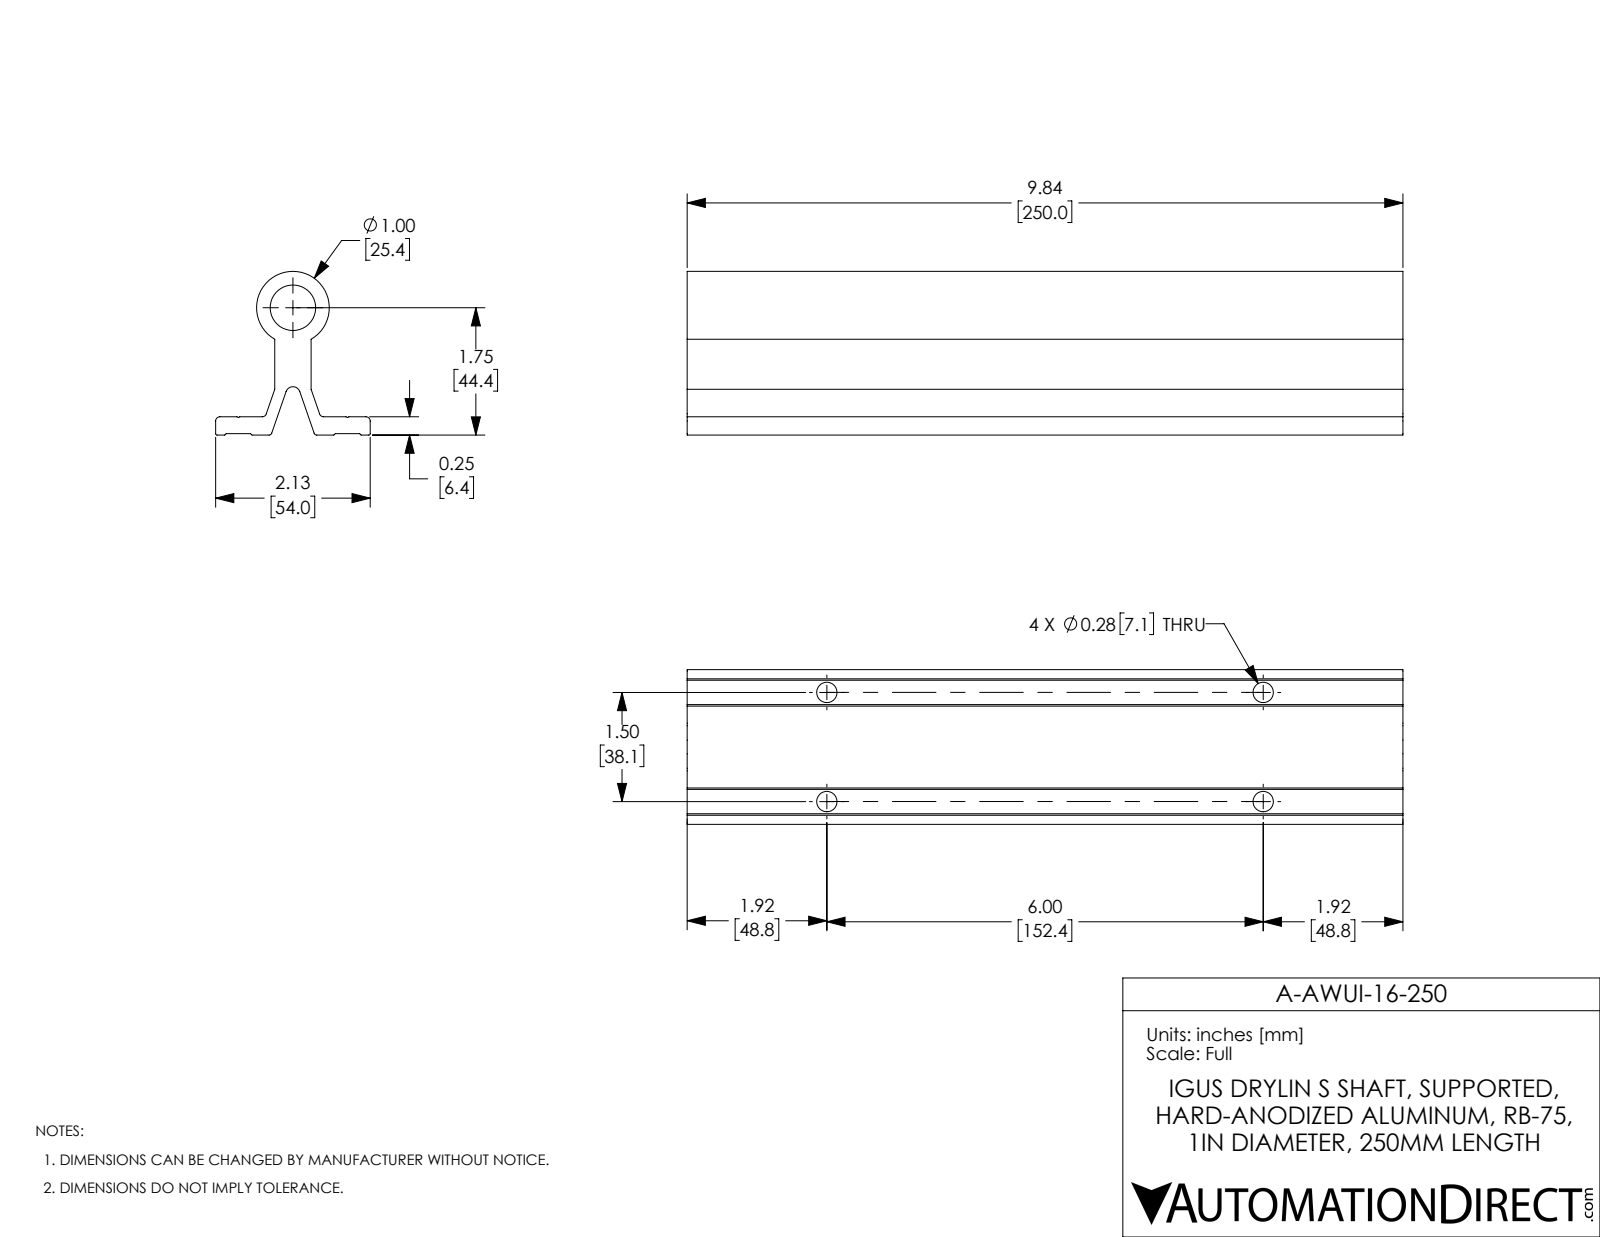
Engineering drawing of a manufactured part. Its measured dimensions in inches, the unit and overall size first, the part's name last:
Units: inches
Overall size (bounding box): 9.843 × 2.25 × 2.126
Round holes (diameter × count): ⌀0.28 ×4, ⌀0.626 ×1
Round bosses / shafts (diameter × count): ⌀1 ×1
Partial cylindrical surfaces — rounded edges, fillets, slot ends (radius × count): R0.059 ×4, R0.02 ×2, R0.039 ×2, R0.1 ×1
Main face-to-face distances: 0.157, 0.252, 0.02, 0.232, 0.813, 2.126, 1.313, 9.843, 1.061, 0.75
Hole centre spacings: 1.5, 6, 6.185
Volume: 12.85 in³ · Surface area: 117.2 in²
Bodies: 1 solid, 56 faces (36 planar, 20 cylindrical, 0 other)
Part name (STEP PRODUCT): A-AWUI-16-250
STEP written by: SolidWorks 2017 (AUTOMOTIVE_DESIGN)
